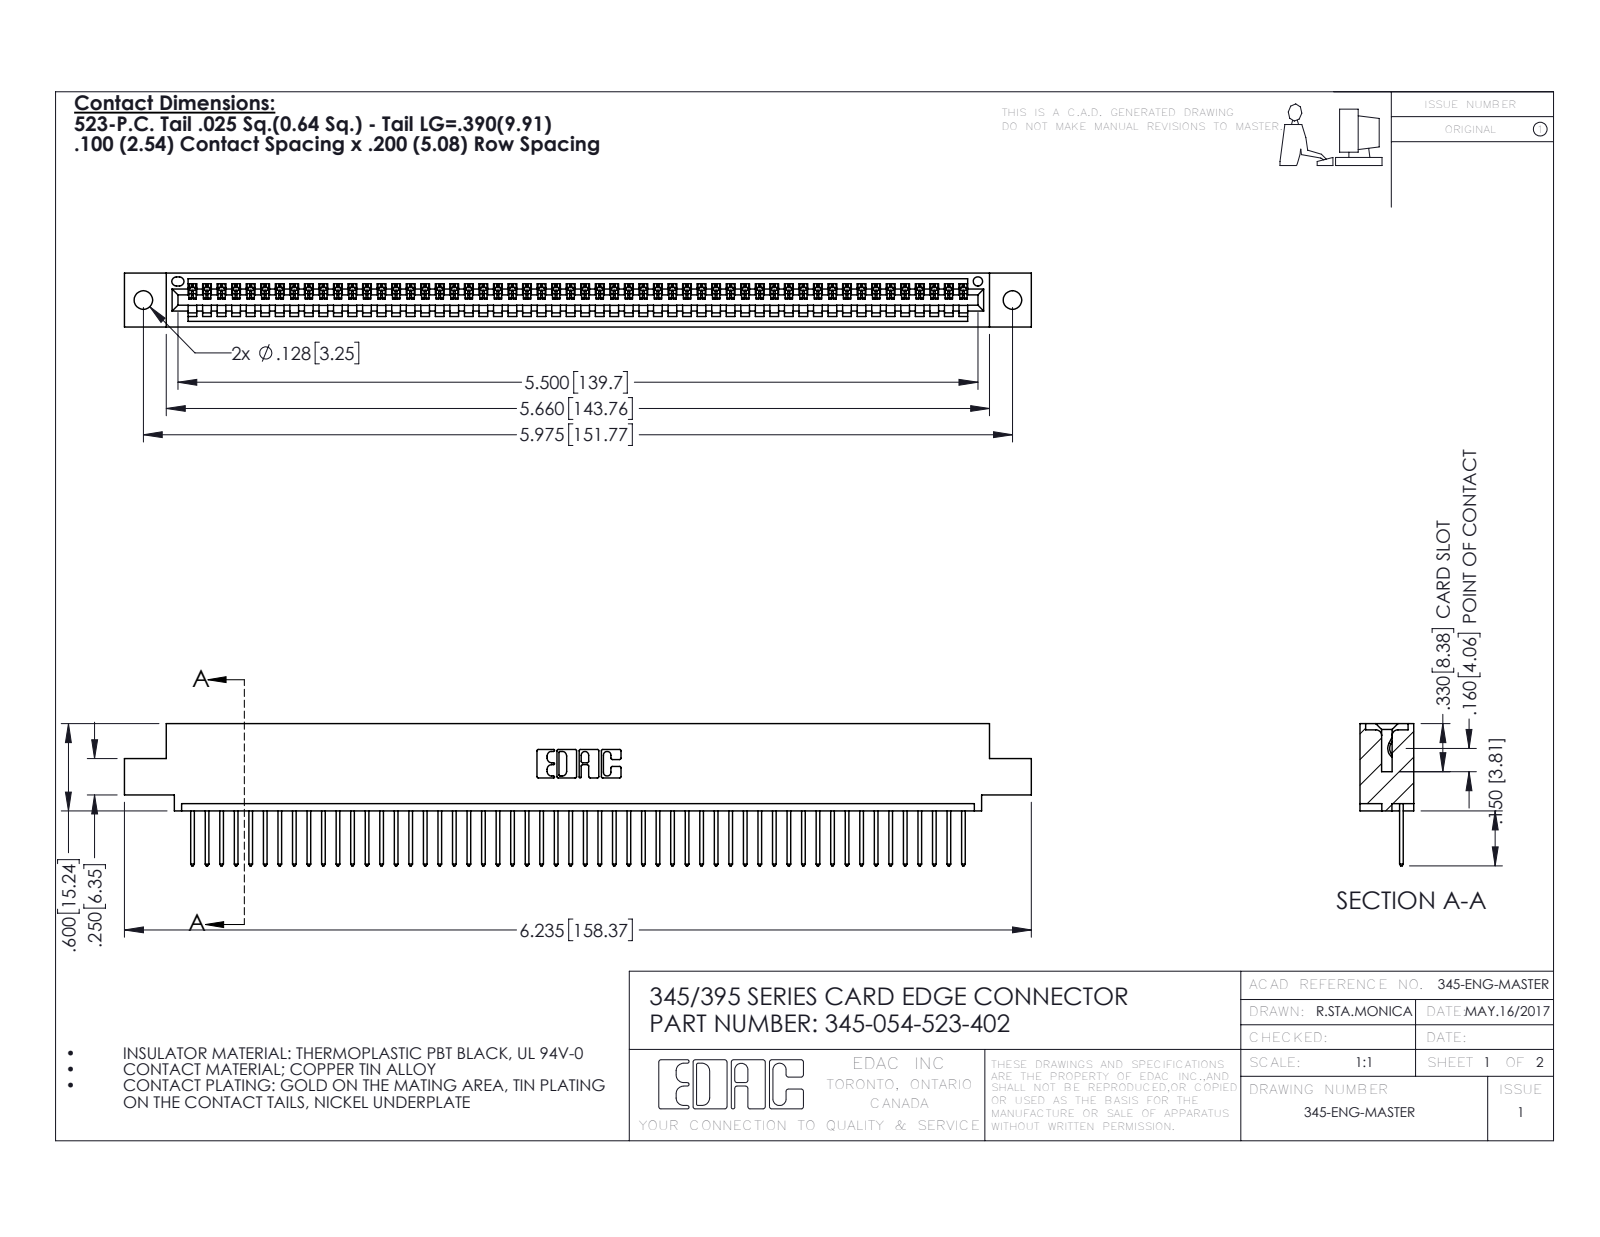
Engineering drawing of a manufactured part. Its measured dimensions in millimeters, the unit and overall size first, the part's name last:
Units: millimetres
Overall size (bounding box): 158.4 × 24.8 × 9.4
Round holes (diameter × count): ⌀3.3 ×2, ⌀1.6 ×1
Partial cylindrical surfaces — rounded edges, fillets, slot ends (radius × count): R0.2 ×108, R0.3 ×108, R0.3 ×22, R0.2 ×6, R0.8 ×6, R0.7 ×3, R0.8 ×2, R1 ×2
Main face-to-face distances: 7.6, 1.8, 9.4, 2.5, 6.9, 0.6, 5.1, 5.7, 3.8, 1.8
Hole centre spacings: 6.9, 145.8, 151.8
Volume: 15 000 mm³ · Surface area: 19 980 mm²
Bodies: 55 solids, 3262 faces (2244 planar, 1018 cylindrical, 0 other)
Part name (STEP PRODUCT): 345 Part_0.110 Offset - 0.128 Dia; 345-054-523-402; 345-292-001_345-293-123
STEP written by: SolidWorks 2016 (CONFIG_CONTROL_DESIGN)
